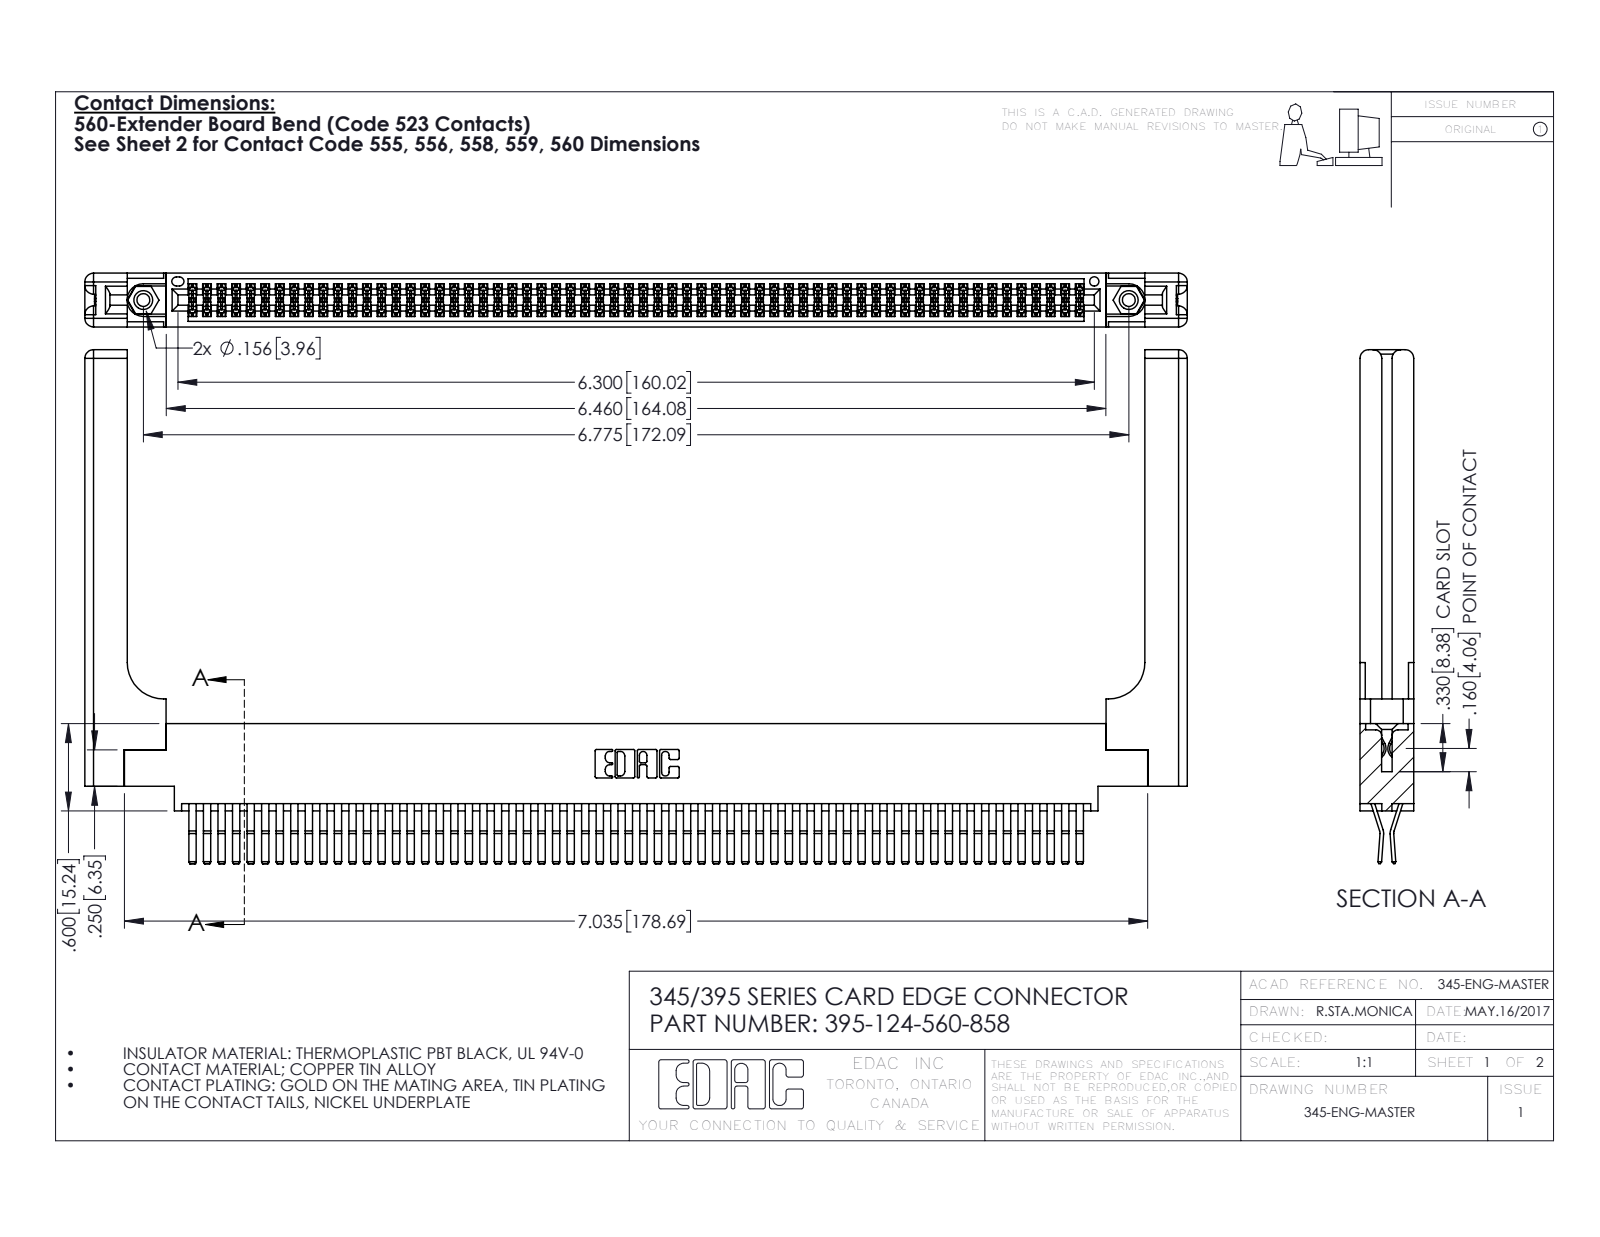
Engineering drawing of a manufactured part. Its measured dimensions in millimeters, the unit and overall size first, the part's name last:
Units: millimetres
Overall size (bounding box): 192.5 × 89.7 × 9.4
Round holes (diameter × count): ⌀2.3 ×2, ⌀3.2 ×2, ⌀4 ×2, ⌀1.6 ×1
Round bosses / shafts (diameter × count): ⌀3.9 ×2
Partial cylindrical surfaces — rounded edges, fillets, slot ends (radius × count): R0.2 ×187, R0.3 ×22, R1.5 ×16, R0.2 ×6, R0.8 ×6, R0.7 ×3, R0.3 ×2, R0.4 ×2
Main face-to-face distances: 1.8, 7.6, 0.6, 9.4, 2.5, 6.9, 5.1, 5.7, 4.4, 3.8
Hole centre spacings: 6.9, 166.1, 172.1
Volume: 28 050 mm³ · Surface area: 36 630 mm²
Bodies: 129 solids, 6834 faces (4324 planar, 2450 cylindrical, 60 other)
Part name (STEP PRODUCT): 345 Part_0.170 Offset - 0.156 Dia-TH; 395-124-560-858; 345-220-058_345-220-058; 345-250-001_345-250-001-102 (+1 more)
STEP written by: SolidWorks 2016 (CONFIG_CONTROL_DESIGN)
